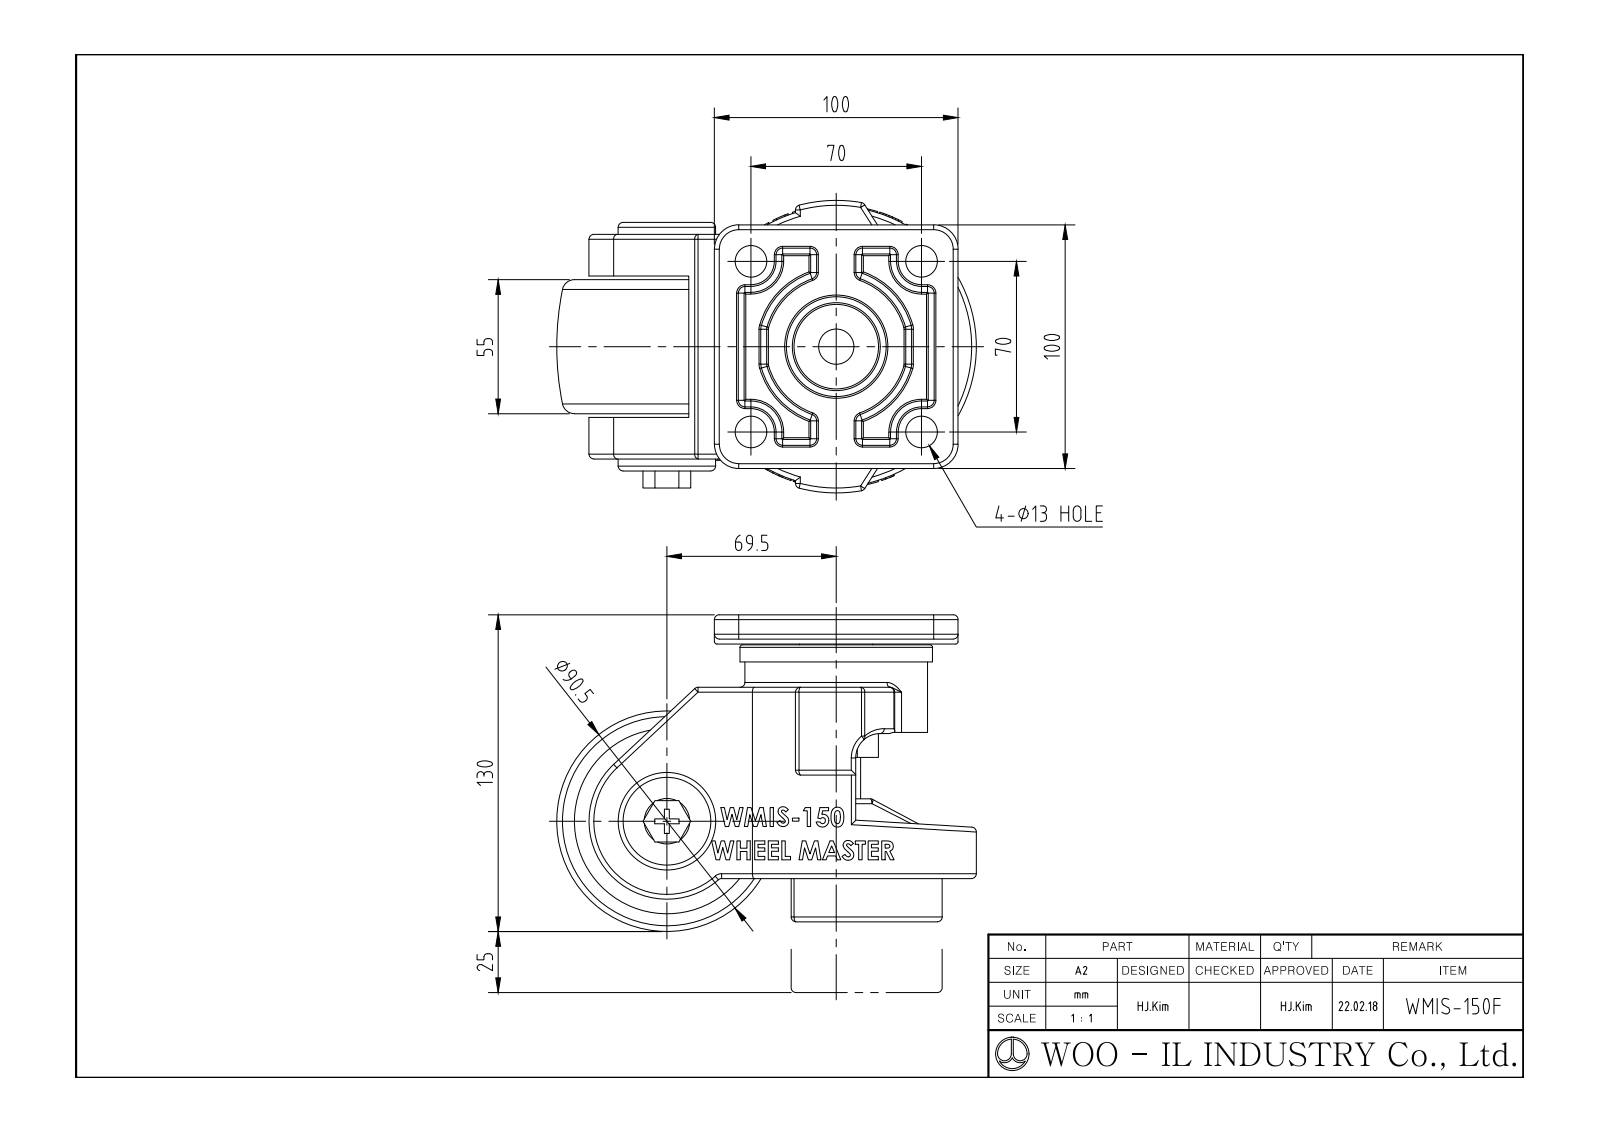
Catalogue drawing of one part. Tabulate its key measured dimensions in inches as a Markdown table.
| quantity | value |
| --- | --- |
| part name | WMIS-150F |
| STEP written by | SolidWorks 2019 (AUTOMOTIVE_DESIGN) |
| units | inches |
| bodies | 1 solid, 887 faces (246 planar, 272 cylindrical, 369 other) |
| overall size | 6.772 × 5.118 × 4.724 |
| volume | 68.9 in³ |
| surface area | 242.6 in² |
| round holes (diameter × count) | 0.512 × 4, 0.27 × 1, 0.335 × 1, 0.394 × 1, 0.571 × 1, 1.291 × 1, 2.114 × 1, 2.492 × 1, 2.52 × 1, 2.949 × 1 |
| round bosses / shafts (diameter × count) | 3.075 × 1, 2.933 × 1, 2.733 × 1, 1.575 × 1, 1.142 × 1, 0.827 × 1, 0.787 × 1, 0.334 × 1 |
| partial cylindrical surfaces (radius × count) | 0.039 × 50, 0.079 × 46, 0.197 × 30, 0.118 × 7, 0.394 × 4, 0.591 × 1, 1.26 × 1, 1.732 × 1 |
| main face-to-face distances | 0.059, 2.224, 0.079, 0.669, 0.157, 2.894, 0.728, 2.953, 0.709, 0.472 |
| hole center spacings | 1.949, 2.756, 3.897, 3.818 |
